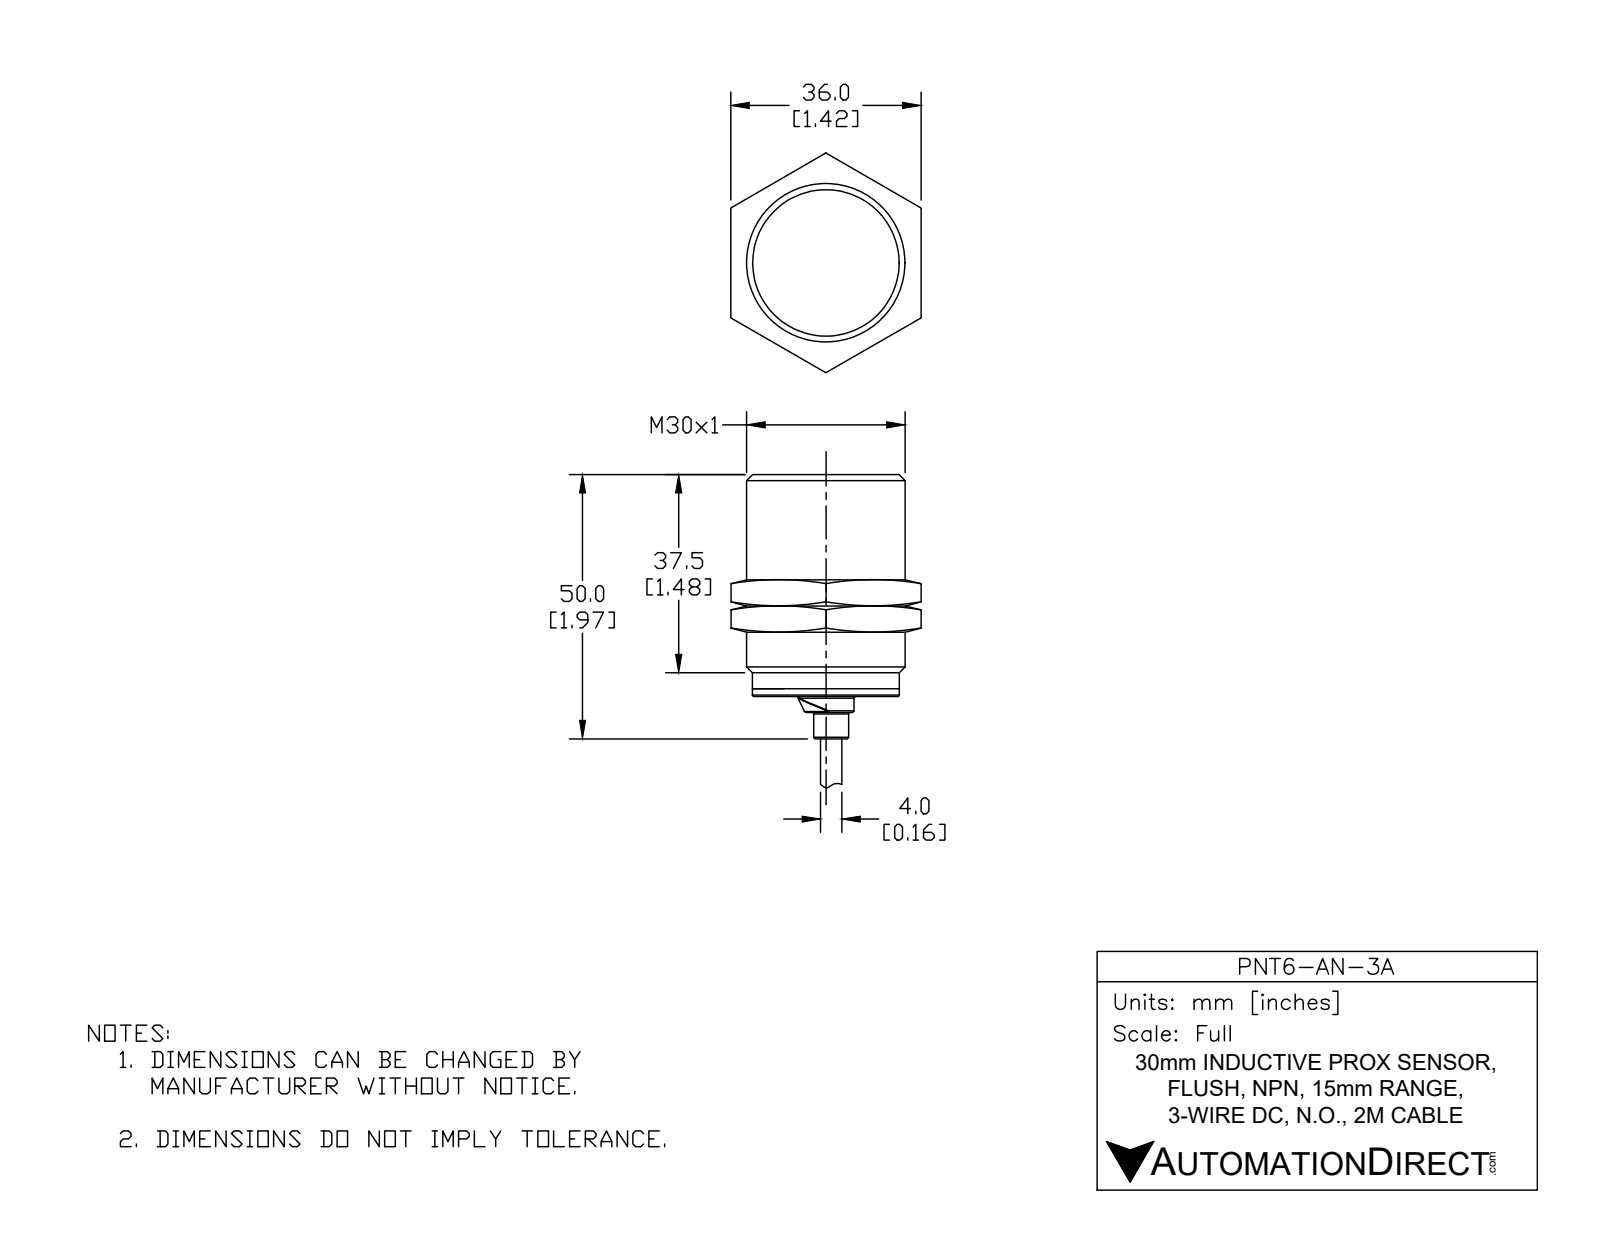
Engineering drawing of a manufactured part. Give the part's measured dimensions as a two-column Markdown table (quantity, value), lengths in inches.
| quantity | value |
| --- | --- |
| part name | PNT6-AN-3A |
| STEP written by | SolidWorks 2017 (AUTOMOTIVE_DESIGN) |
| units | inches |
| bodies | 1 solid, 77 faces (15 planar, 30 cylindrical, 32 other) |
| overall size | 3.969 × 1.181 × 1.181 |
| volume | 1.84 in³ |
| surface area | 9.715 in² |
| round holes (diameter × count) | 0.162 × 1 |
| round bosses / shafts (diameter × count) | 0.049 × 6, 1.181 × 1, 1.095 × 1, 1.094 × 1, 0.417 × 1, 0.26 × 1, 0.157 × 1 |
| partial cylindrical surfaces (radius × count) | 0.077 × 1 |
| main face-to-face distances | 1.654, 1.772, 0.118, 1.969, 0.315, 0.197, 3.969, 2.315, 2.197, 2 |
